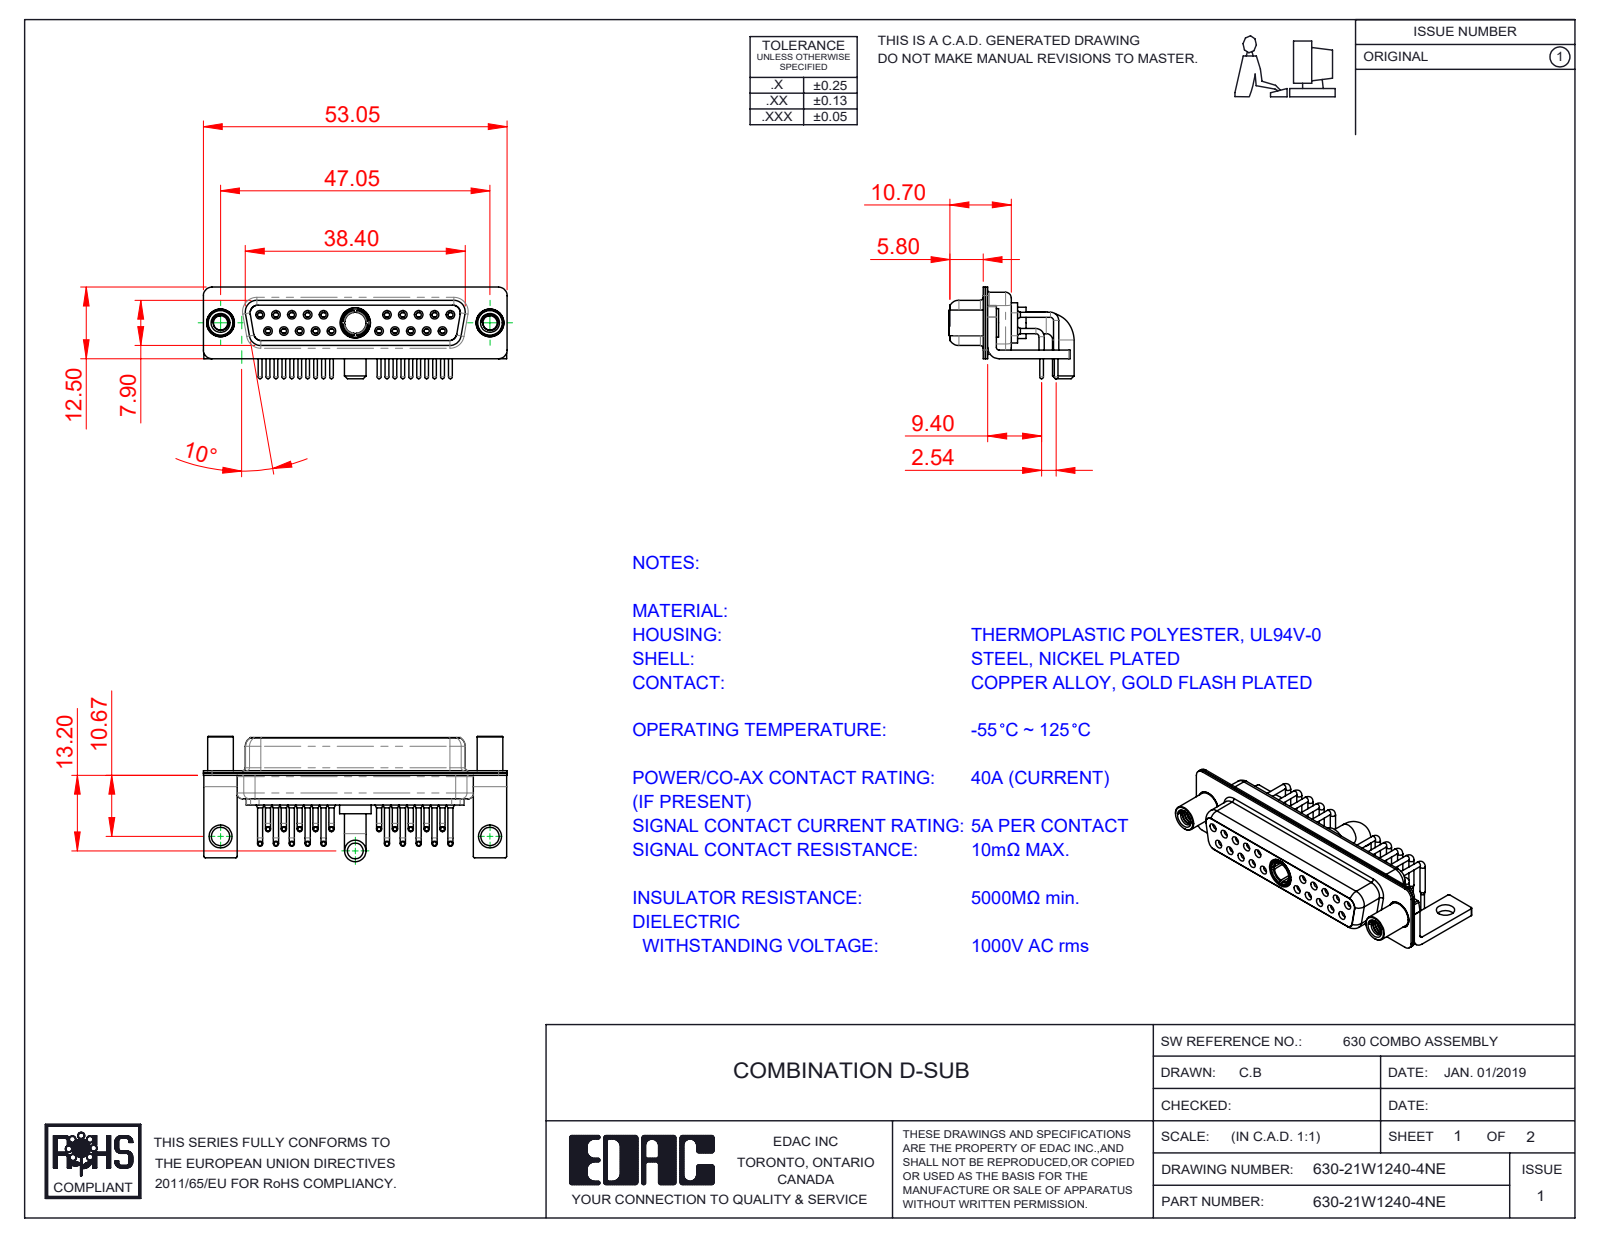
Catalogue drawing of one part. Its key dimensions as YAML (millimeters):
part_name: "630Combo Contact Row 2; Power Socket_40A RA; 630Combo Stabilizer Bracket; 630Combo Shell Front_25 Contacts (+5 more)"
step_written_by: "SolidWorks 2020 (CONFIG_CONTROL_DESIGN)"
units: millimeters
bodies: {solids: 29, faces: 1515, planar: 418, cylindrical: 694, other: 403}
overall_size: [53.05, 21.88, 16]
volume: 4483
surface_area: 10319
round_holes:
  - {diameter: 0.9, count: 20}
  - {diameter: 1.1, count: 20}
  - {diameter: 1.5, count: 20}
  - {diameter: 2, count: 20}
  - {diameter: 1.6, count: 10}
  - {diameter: 1.7, count: 10}
  - {diameter: 4.85, count: 3}
  - {diameter: 2.5, count: 2}
  - {diameter: 3.2, count: 2}
  - {diameter: 4, count: 2}
  - {diameter: 4.05, count: 2}
  - {diameter: 3.7, count: 1}
round_bosses_or_shafts:
  - {diameter: 0.9, count: 20}
  - {diameter: 0.65, count: 20}
  - {diameter: 1.6, count: 10}
  - {diameter: 5, count: 2}
  - {diameter: 4.95, count: 2}
  - {diameter: 4.8, count: 2}
  - {diameter: 4.5, count: 2}
  - {diameter: 3.75, count: 2}
partial_cylinders:
  - {radius: 0.25, count: 16}
  - {radius: 1.5, count: 16}
  - {radius: 2, count: 13}
  - {radius: 1.35, count: 8}
  - {radius: 1.6, count: 8}
  - {radius: 0.5, count: 5}
  - {radius: 0.6, count: 4}
  - {radius: 0.65, count: 4}
face_to_face_distances: [0.4, 0.45, 1.4, 8.45, 0.8, 1.8, 8.9, 6.2, 7.05, 1.5]
hole_center_spacings: [3.16, 2.77, 5.54, 8.31, 5.04, 19.39, 20.97, 22.16]
